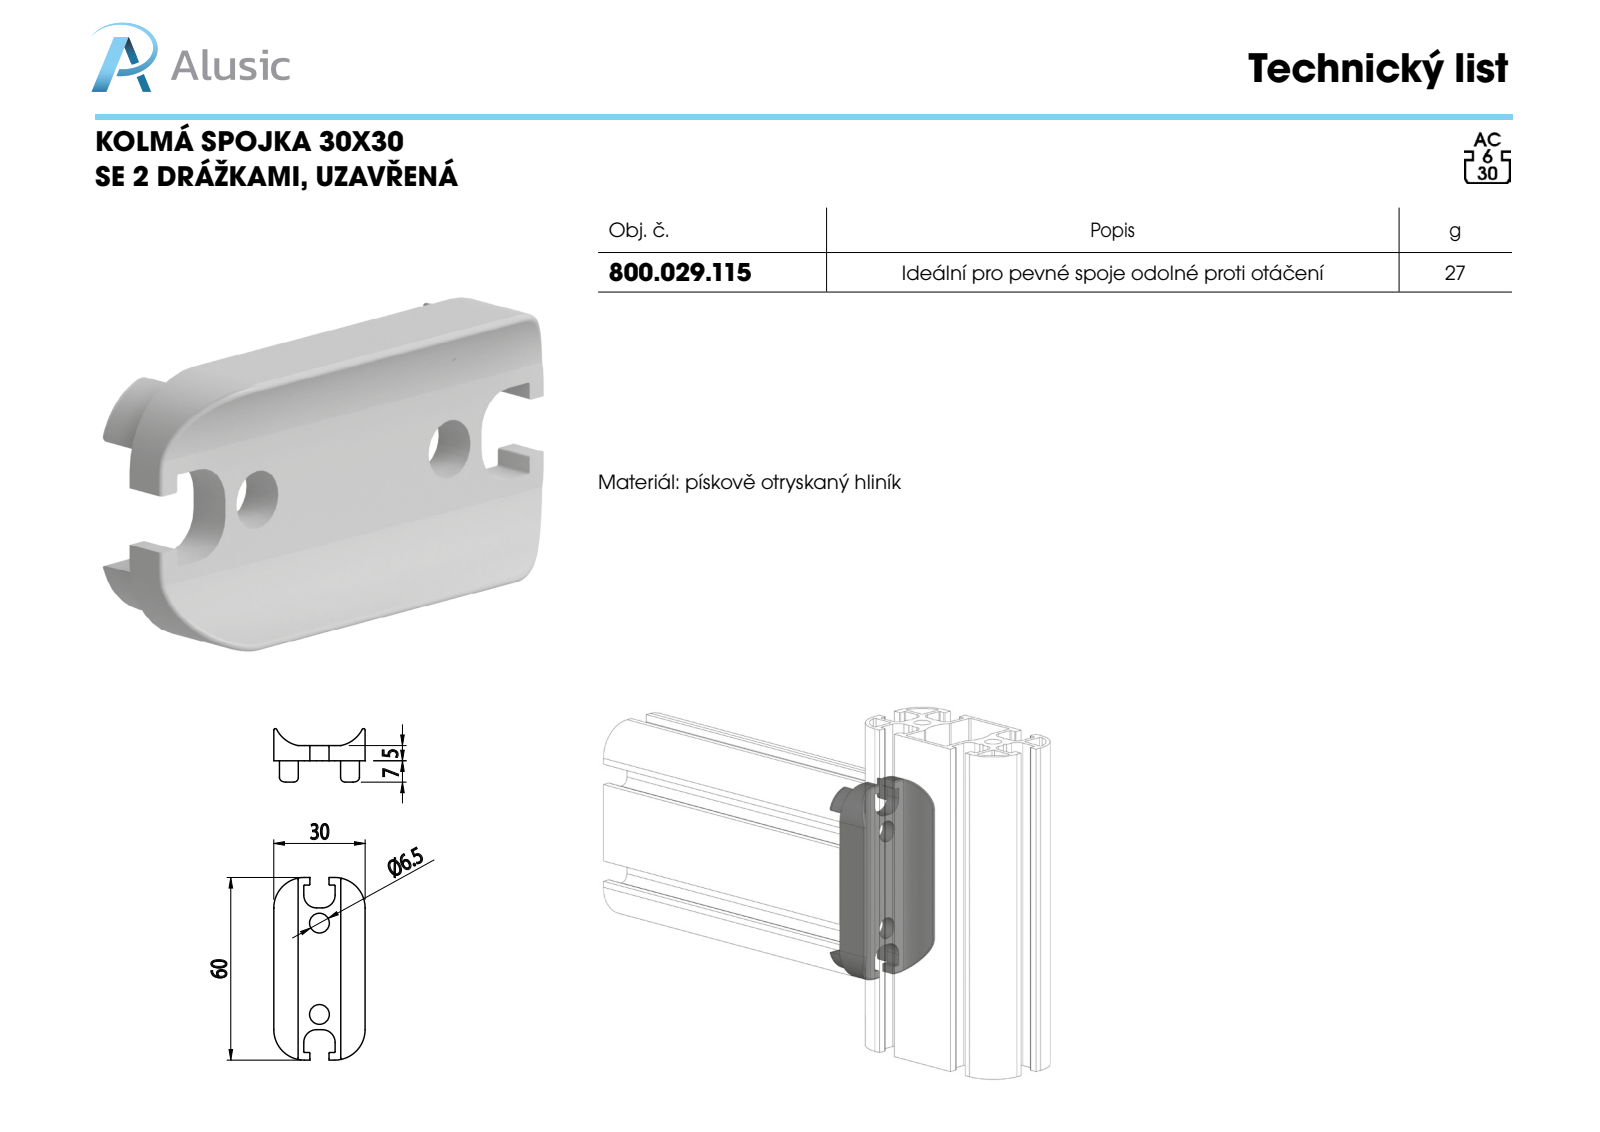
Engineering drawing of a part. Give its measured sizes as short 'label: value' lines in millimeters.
name: 800.029.115
written by: SolidWorks 2012 (CONFIG_CONTROL_DESIGN)
unit: mm
bodies: 1 solid, 112 faces (34 planar, 54 cylindrical, 24 other)
size: 60 × 30 × 17.58
volume: 9 918 mm³; area: 5 542 mm²
holes: 2× ⌀6.5
rounds: 12× R0.1, 8× R0.25, 4× R0.5, 4× R1.5, 4× R4.2, 4× R8.4, 4× R10, 2× R10.2
face distances: 5, 30, 8.05, 21.95, 13.9, 43.9, 9.85, 20.15, 1.8, 12.1
hole spacings: 30
